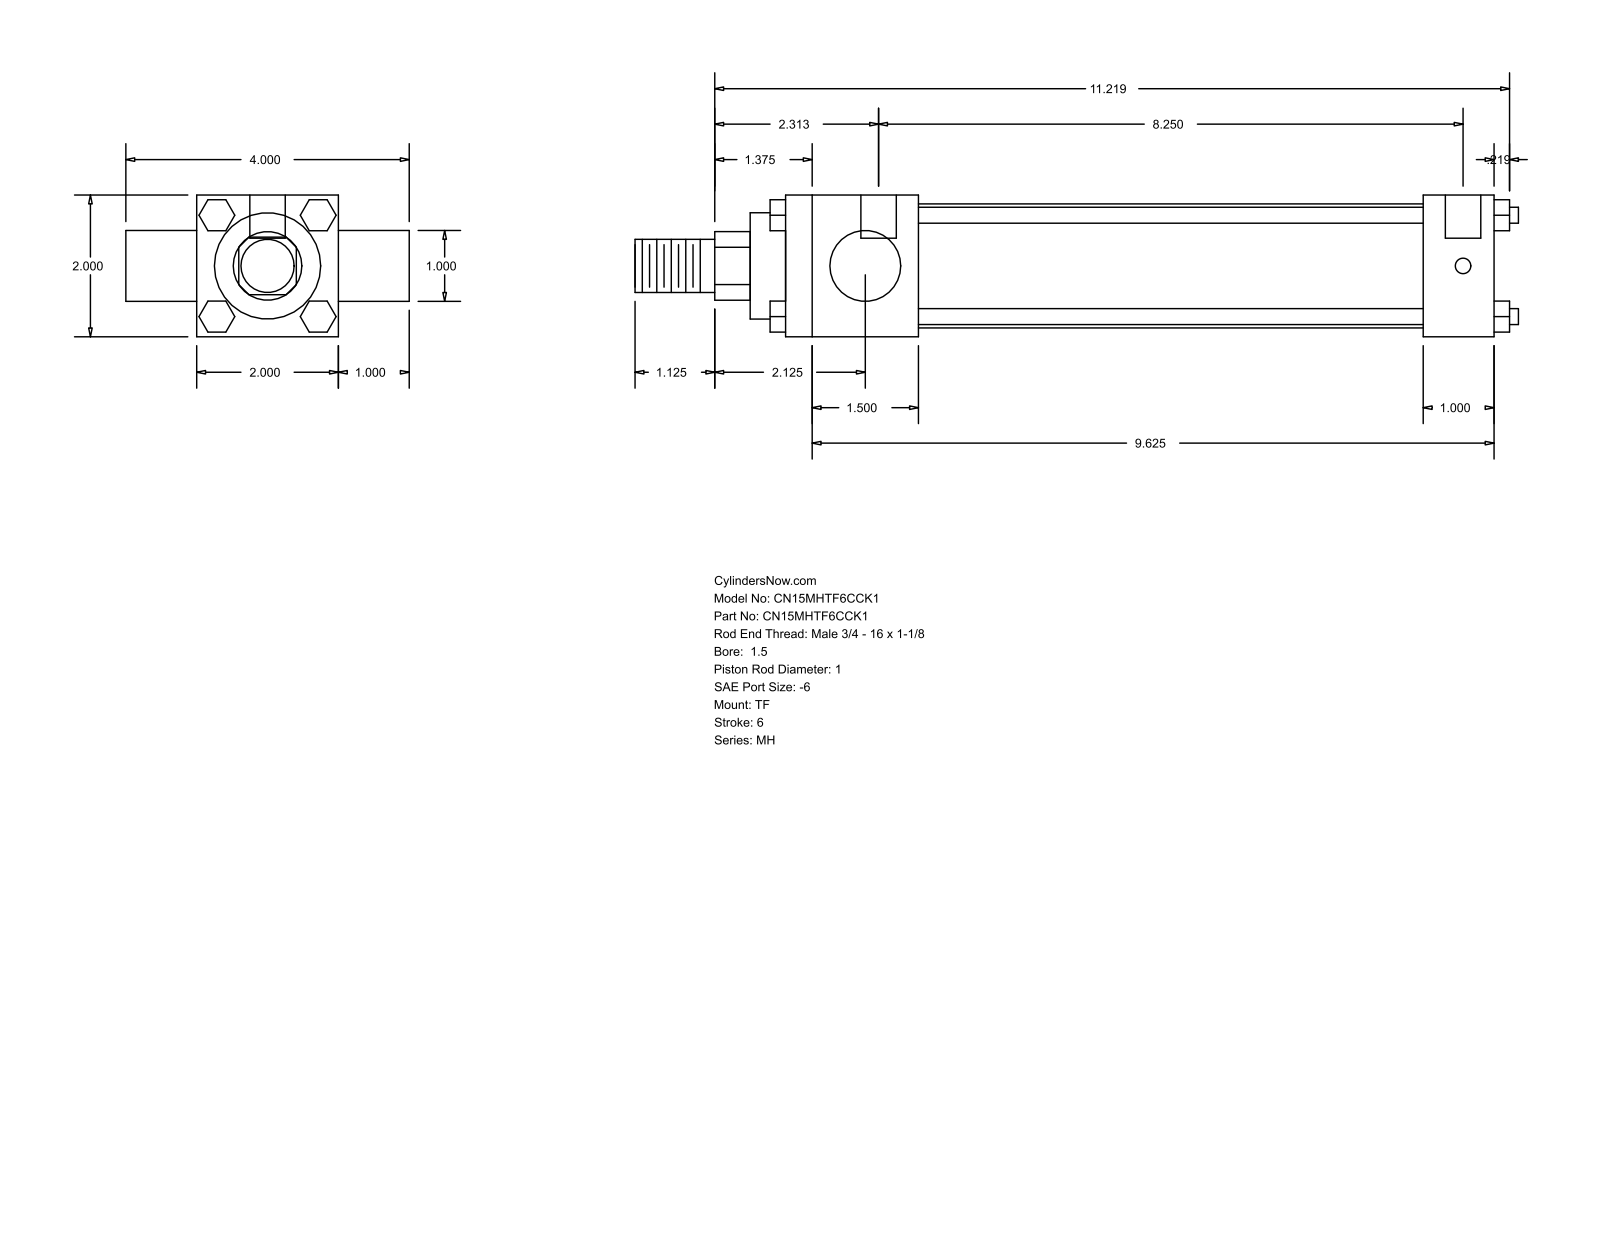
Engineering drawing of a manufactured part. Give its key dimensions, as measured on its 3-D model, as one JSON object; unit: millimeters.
{"part_name": "MH_TF__0150_1", "step_written_by": "GSSL Pune (CONFIG_CONTROL_DESIGN)", "units": "millimeters", "bodies": {"solids": 0, "faces": 120, "planar": 92, "cylindrical": 28, "other": 0}, "overall_size": [316.71, 101.6, 50.8], "round_holes": [[5.56, 3], [12.7, 2]], "round_bosses_or_shafts": [[5.71, 4], [25.4, 2], [44.45, 1], [38.1, 1], [19.05, 1]], "partial_cylinders_radius": [[12.29, 1]], "face_to_face_distances": [50.8, 25.4, 254, 76.2, 47.63, 206.37, 228.6, 180.97, 101.6, 12.7], "hole_center_spacings": [3.18, 209.55, 212.73]}
